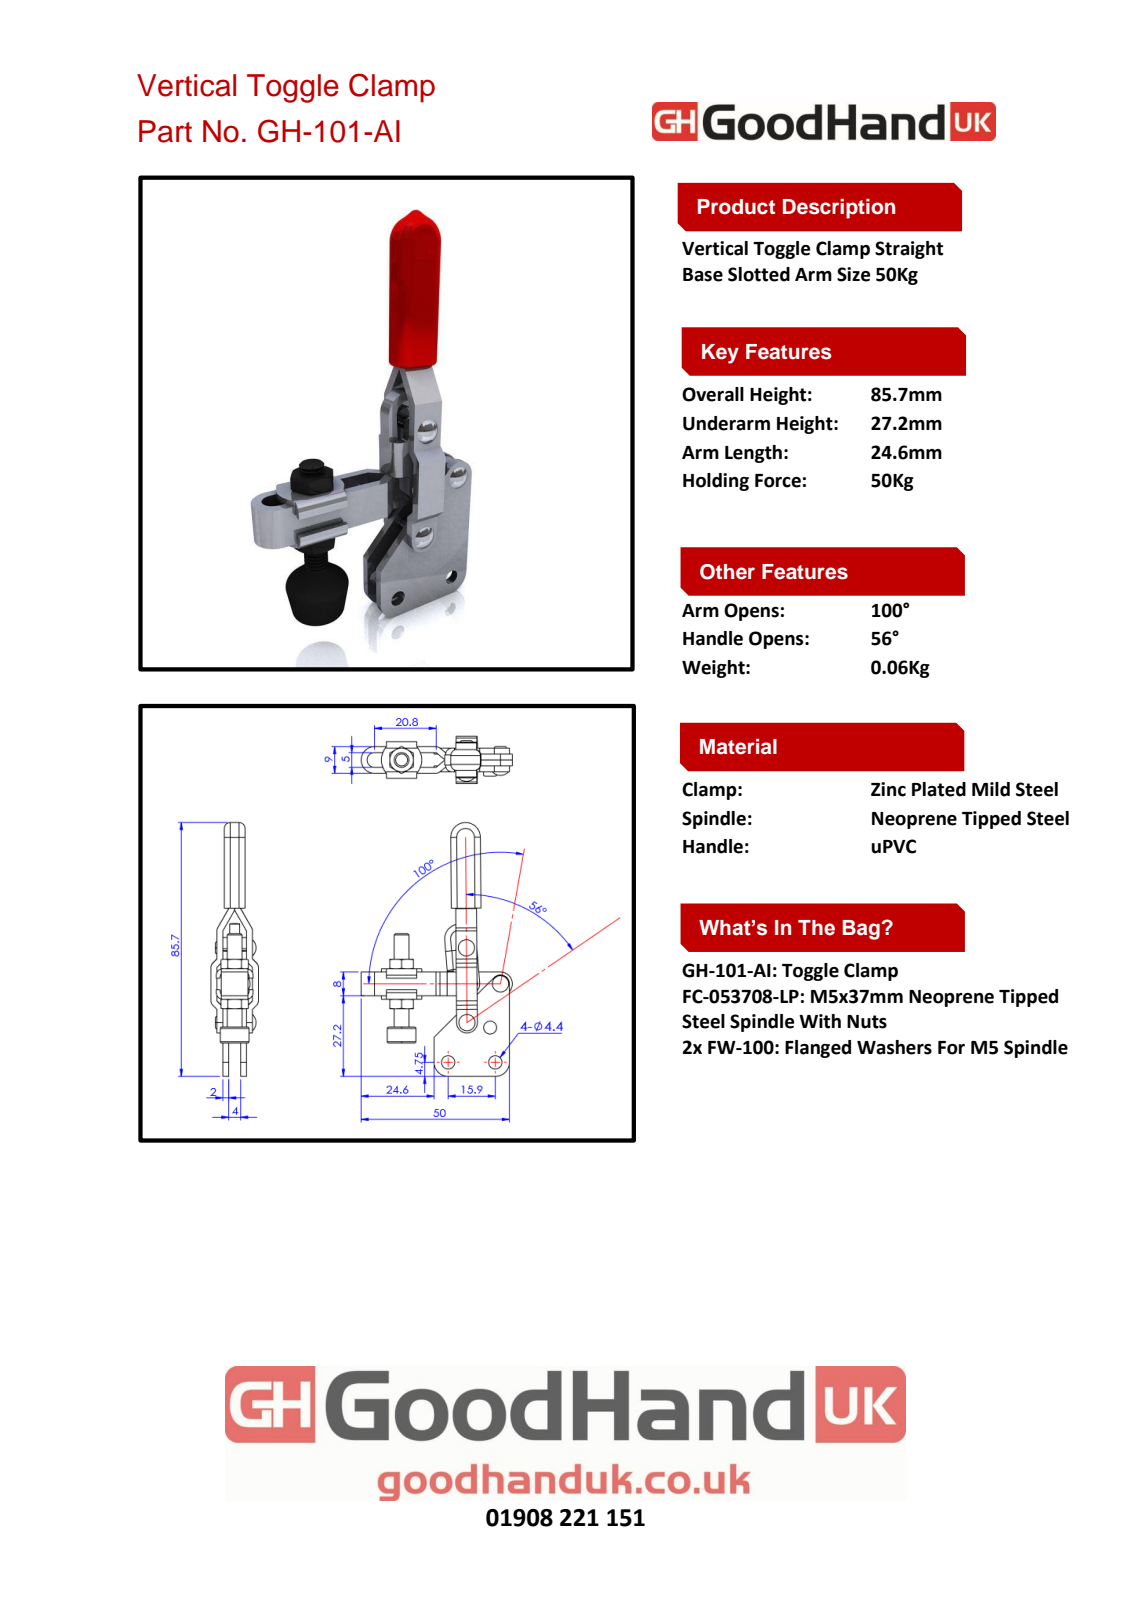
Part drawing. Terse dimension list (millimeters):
name: 1101AI09-1-1^GH-101-AI; GH-101-AI; Group2^GH-101-AI; Group3^GH-101-AI (+2 more)
written by: SolidWorks 2016 (CONFIG_CONTROL_DESIGN)
unit: mm
bodies: 5 solids, 342 faces (186 planar, 112 cylindrical, 44 other)
size: 85.7 × 51 × 16
volume: 9 756 mm³; area: 10 471 mm²
holes: 4× ⌀2.5, 2× ⌀4.5
bosses: 2× ⌀3, 1× ⌀9.65, 1× ⌀5
rounds: 12× R2.01, 6× R1, 4× R0.1, 4× R2.1, 4× R2.2, 3× R3.5, 2× R2.09, 2× R3
face distances: 2, 6, 8, 1.5, 4, 0.5, 8.5, 7, 5.5, 2.5
hole spacings: 10.5, 12.2, 13.11, 14.84, 15.9, 16.46, 16.74, 17.29
